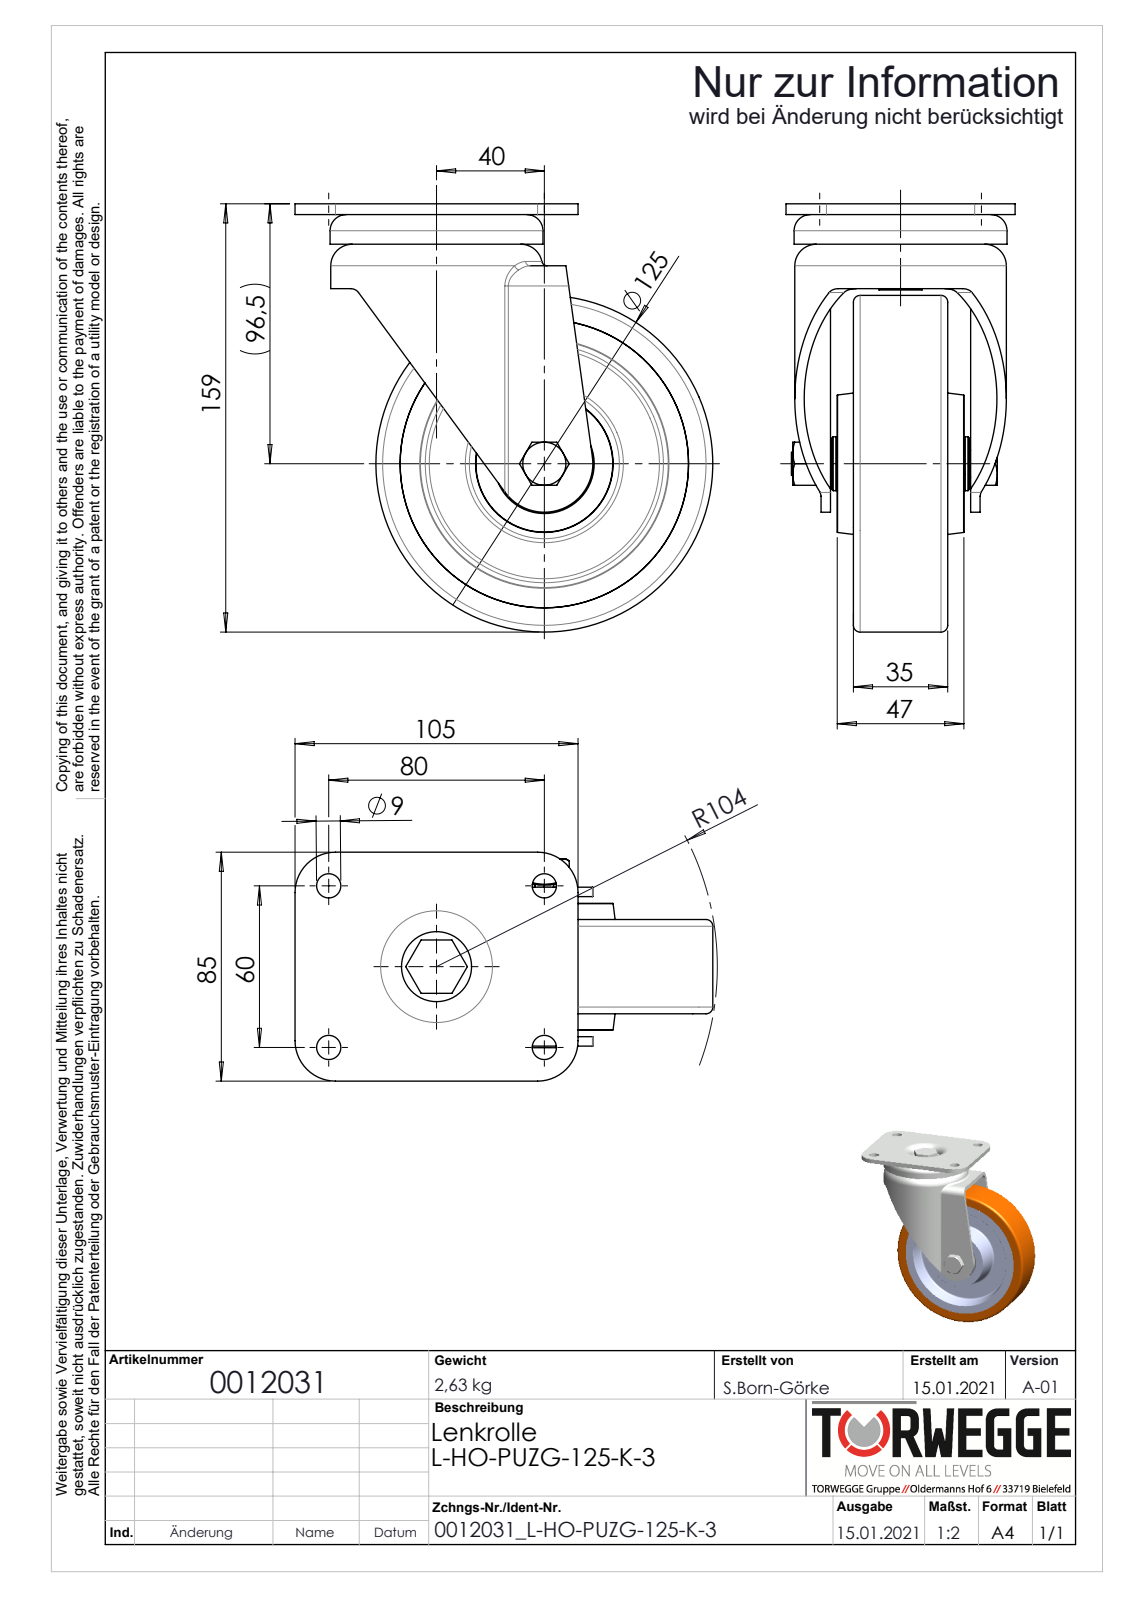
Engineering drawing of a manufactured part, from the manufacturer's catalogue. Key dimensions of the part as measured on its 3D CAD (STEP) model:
Part name (STEP PRODUCT): 0012031
STEP written by: SolidWorks 2018 (AUTOMOTIVE_DESIGN)
Units: millimetres
Bodies: 21 solids, 432 faces (127 planar, 122 cylindrical, 183 other)
Overall size (bounding box): 159 × 155 × 85
Volume: 487 115 mm³ · Surface area: 164 511 mm²
Round holes (diameter × count): ⌀9 ×4, ⌀16 ×2, ⌀8.5 ×1, ⌀10 ×1, ⌀10.5 ×1, ⌀14 ×1, ⌀15 ×1, ⌀16.2 ×1, ⌀21 ×1, ⌀25 ×1, ⌀29 ×1, ⌀35 ×1
Round bosses / shafts (diameter × count): ⌀125 ×1, ⌀79 ×1, ⌀20 ×1, ⌀18 ×1
Partial cylindrical surfaces — rounded edges, fillets, slot ends (radius × count): R15 ×4, R2 ×2, R4 ×2, R7.5 ×2, R3.5 ×1, R18 ×1, R35.75 ×1, R39.25 ×1
Main face-to-face distances: 3.5, 15, 11, 26, 14, 21, 47, 6, 4, 22.5
Hole centre spacings: 50, 60, 80, 100
